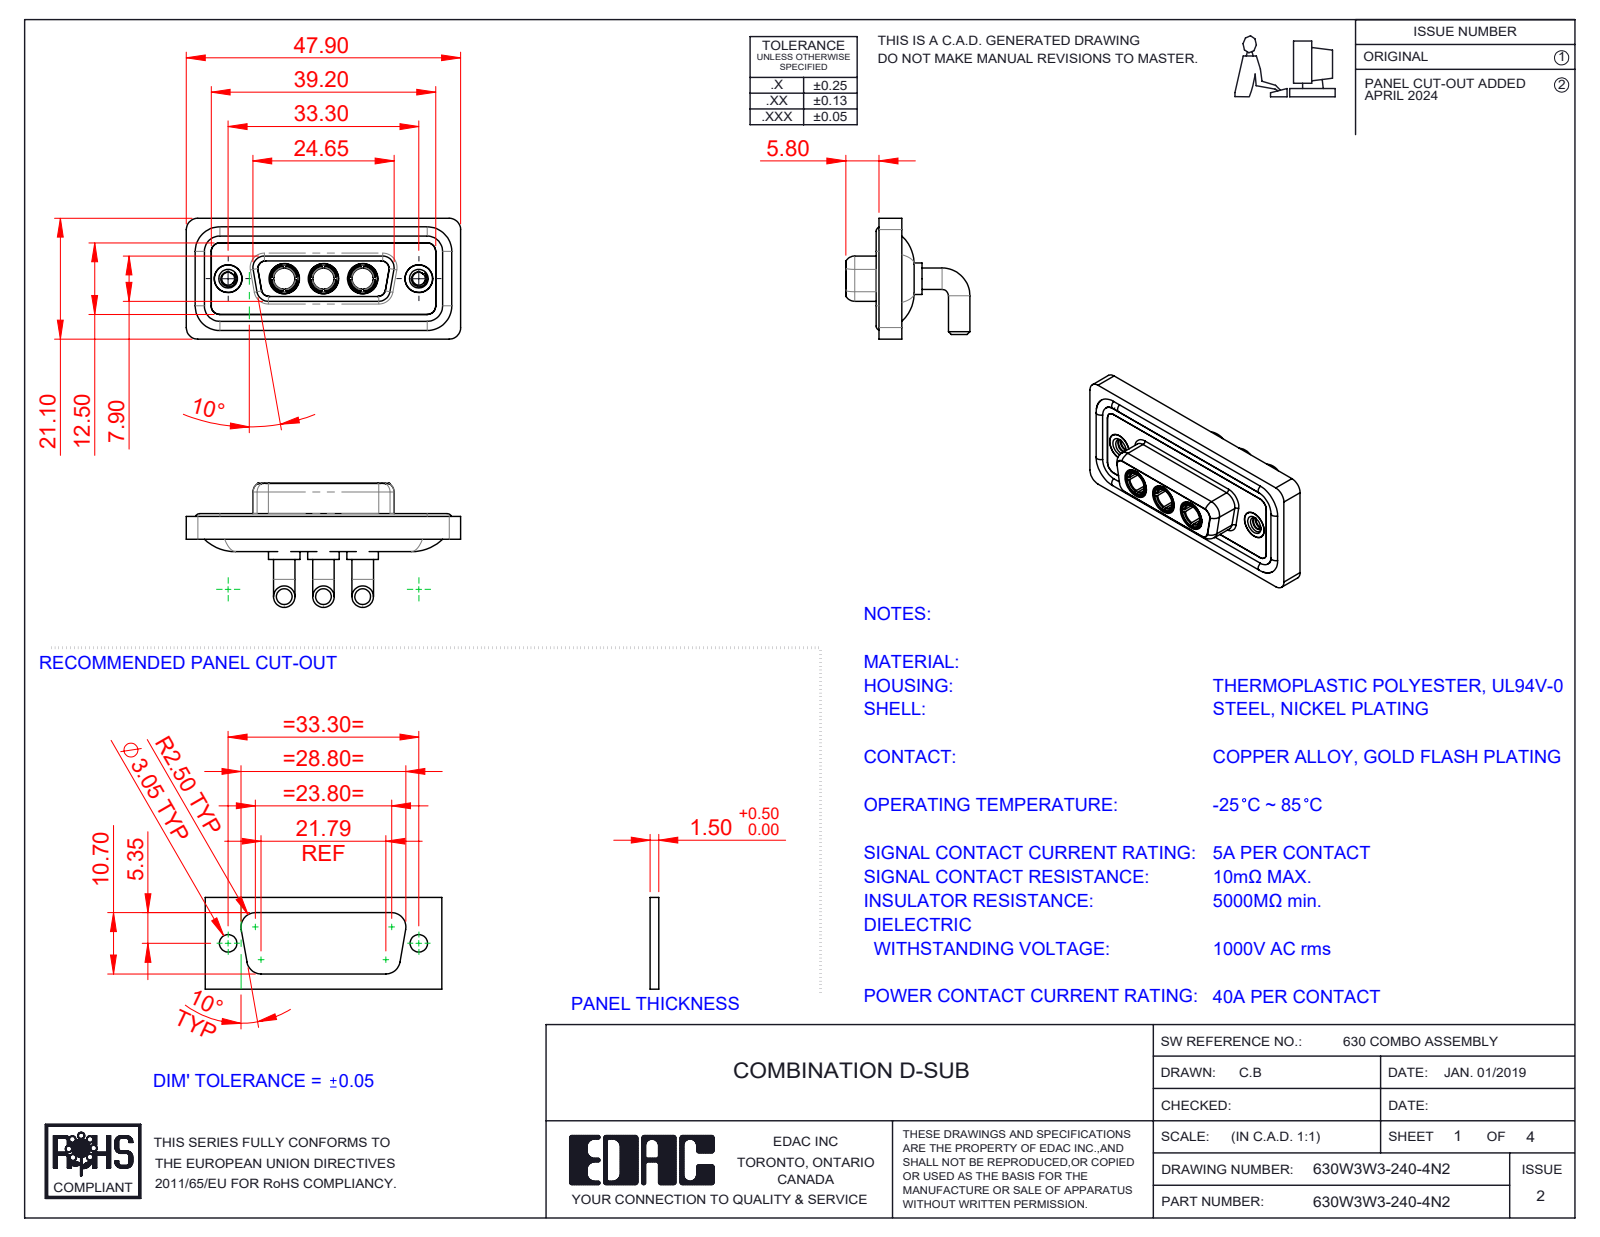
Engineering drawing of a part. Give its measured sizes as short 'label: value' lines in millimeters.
name: 630W3W3-140-4N2; 630Combo Housing_3W3; 630Combo Threaded Rivet_2; 630Combo Shell Front_15 Contacts (+3 more)
written by: SolidWorks 2023 (CONFIG_CONTROL_DESIGN)
unit: mm
bodies: 13 solids, 620 faces (192 planar, 263 cylindrical, 165 other)
size: 47.9 × 21.68 × 21.1
volume: 6 398 mm³; area: 10 103 mm²
holes: 5× ⌀4.85, 3× ⌀3.7, 3× ⌀5.3, 2× ⌀2.26, 2× ⌀4, 2× ⌀4.05, 2× ⌀5
bosses: 6× ⌀3.75, 4× ⌀1.6, 3× ⌀5.5, 3× ⌀5.2, 3× ⌀4.96, 3× ⌀4.75, 2× ⌀4.95, 2× ⌀4.8
rounds: 20× R2, 18× R1.5, 12× R1.35, 8× R1.6, 4× R0.25, 4× R0.5, 4× R0.6, 4× R0.65
face distances: 0.4, 1.8, 1.1, 1.6, 2.9, 2.5, 3.1, 3.7, 4.1, 1.5
hole spacings: 6.85, 9.8, 16.65, 23.5, 13.7, 33.3
